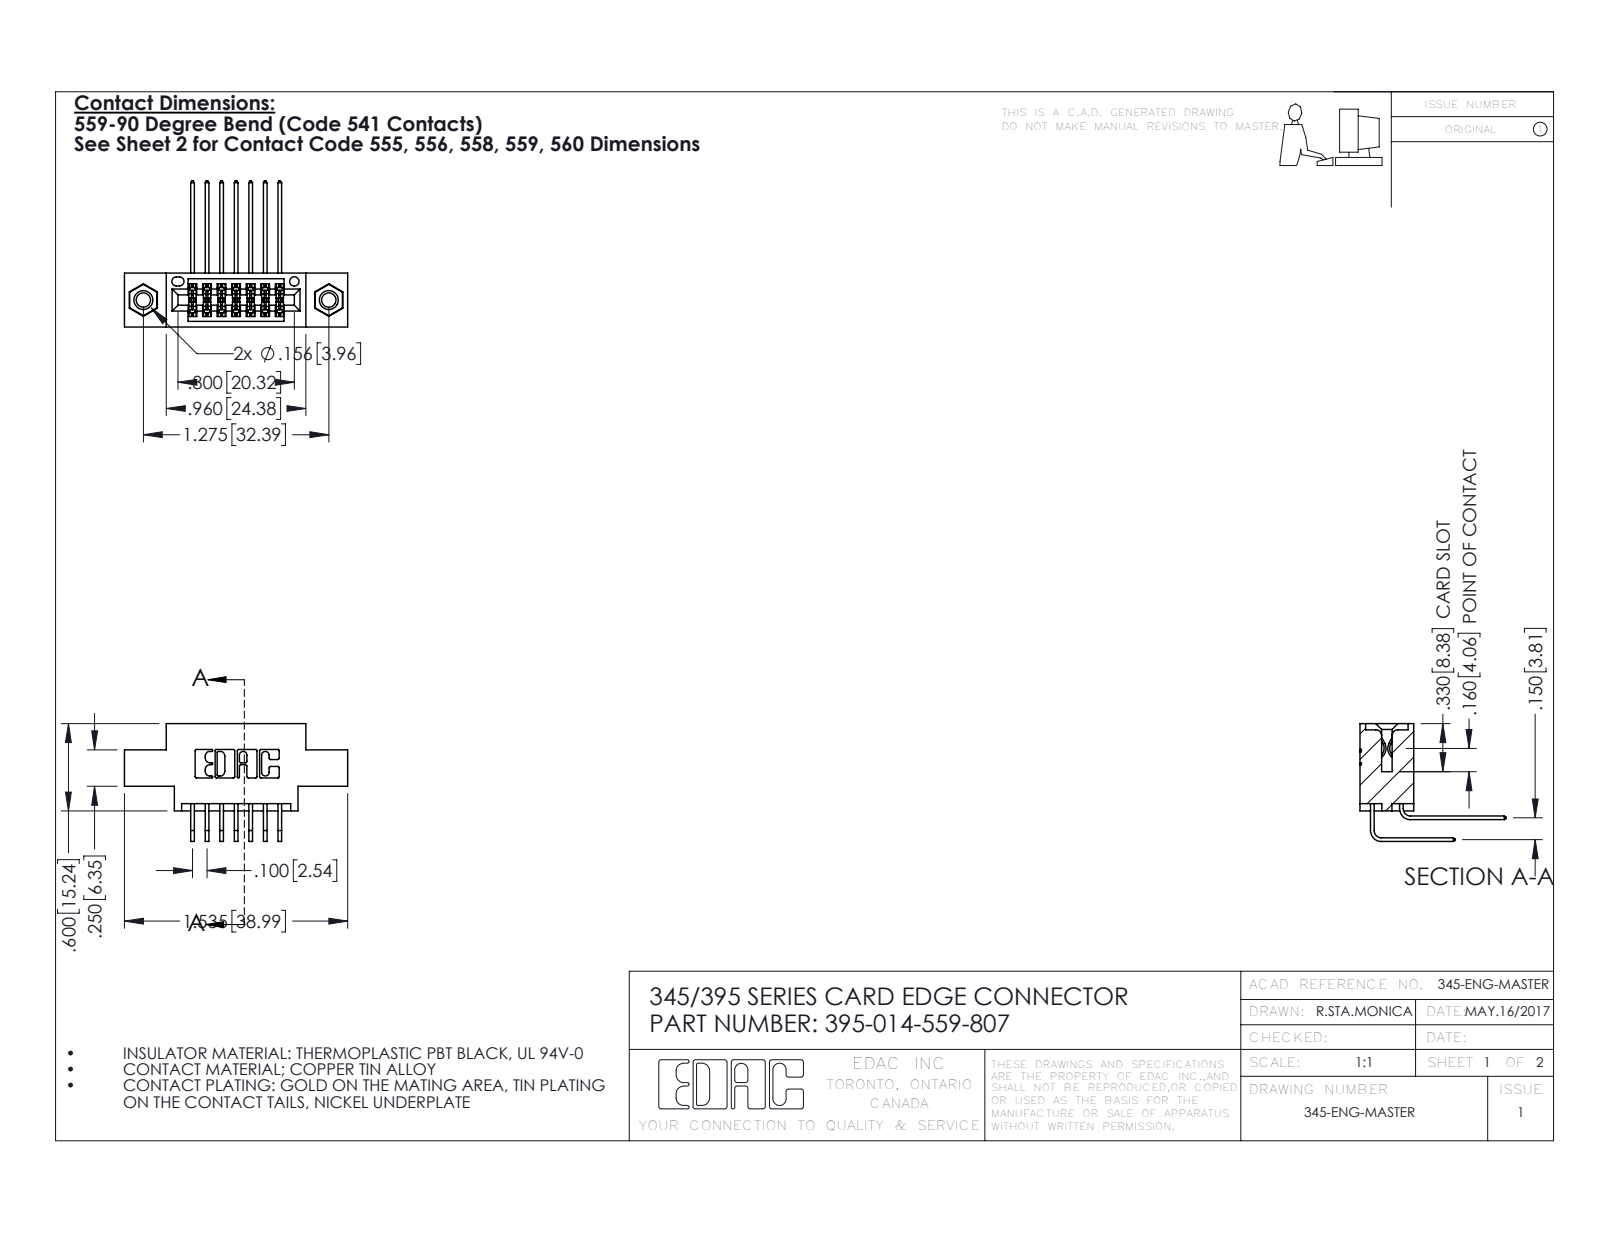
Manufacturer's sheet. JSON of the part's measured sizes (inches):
{"part_name": "395-014-559-807; 345-292-001_559 Tail - 2; 345-250-001_345-250-005-103; 345-292-001_558 559 Tail - 1 (+1 more)", "step_written_by": "SolidWorks 2016 (CONFIG_CONTROL_DESIGN)", "units": "inches", "bodies": {"solids": 17, "faces": 918, "planar": 606, "cylindrical": 296, "other": 16}, "overall_size": [1.535, 1.005, 0.809], "volume_in3": 0.208, "surface_area_in2": 7.631, "round_holes": [[0.098, 2], [0.125, 2], [0.156, 2], [0.064, 1]], "round_bosses_or_shafts": [[0.155, 2]], "partial_cylinders_radius": [[0.006, 22], [0.01, 22], [0.007, 6], [0.031, 6], [0.026, 3], [0.014, 2], [0.019, 2], [0.022, 2]], "face_to_face_distances": [0.2, 0.37, 0.072, 0.298, 0.1, 0.15, 0.098, 0.272, 0.025, 0.3], "hole_center_spacings": [0.27, 1.045, 1.275]}
